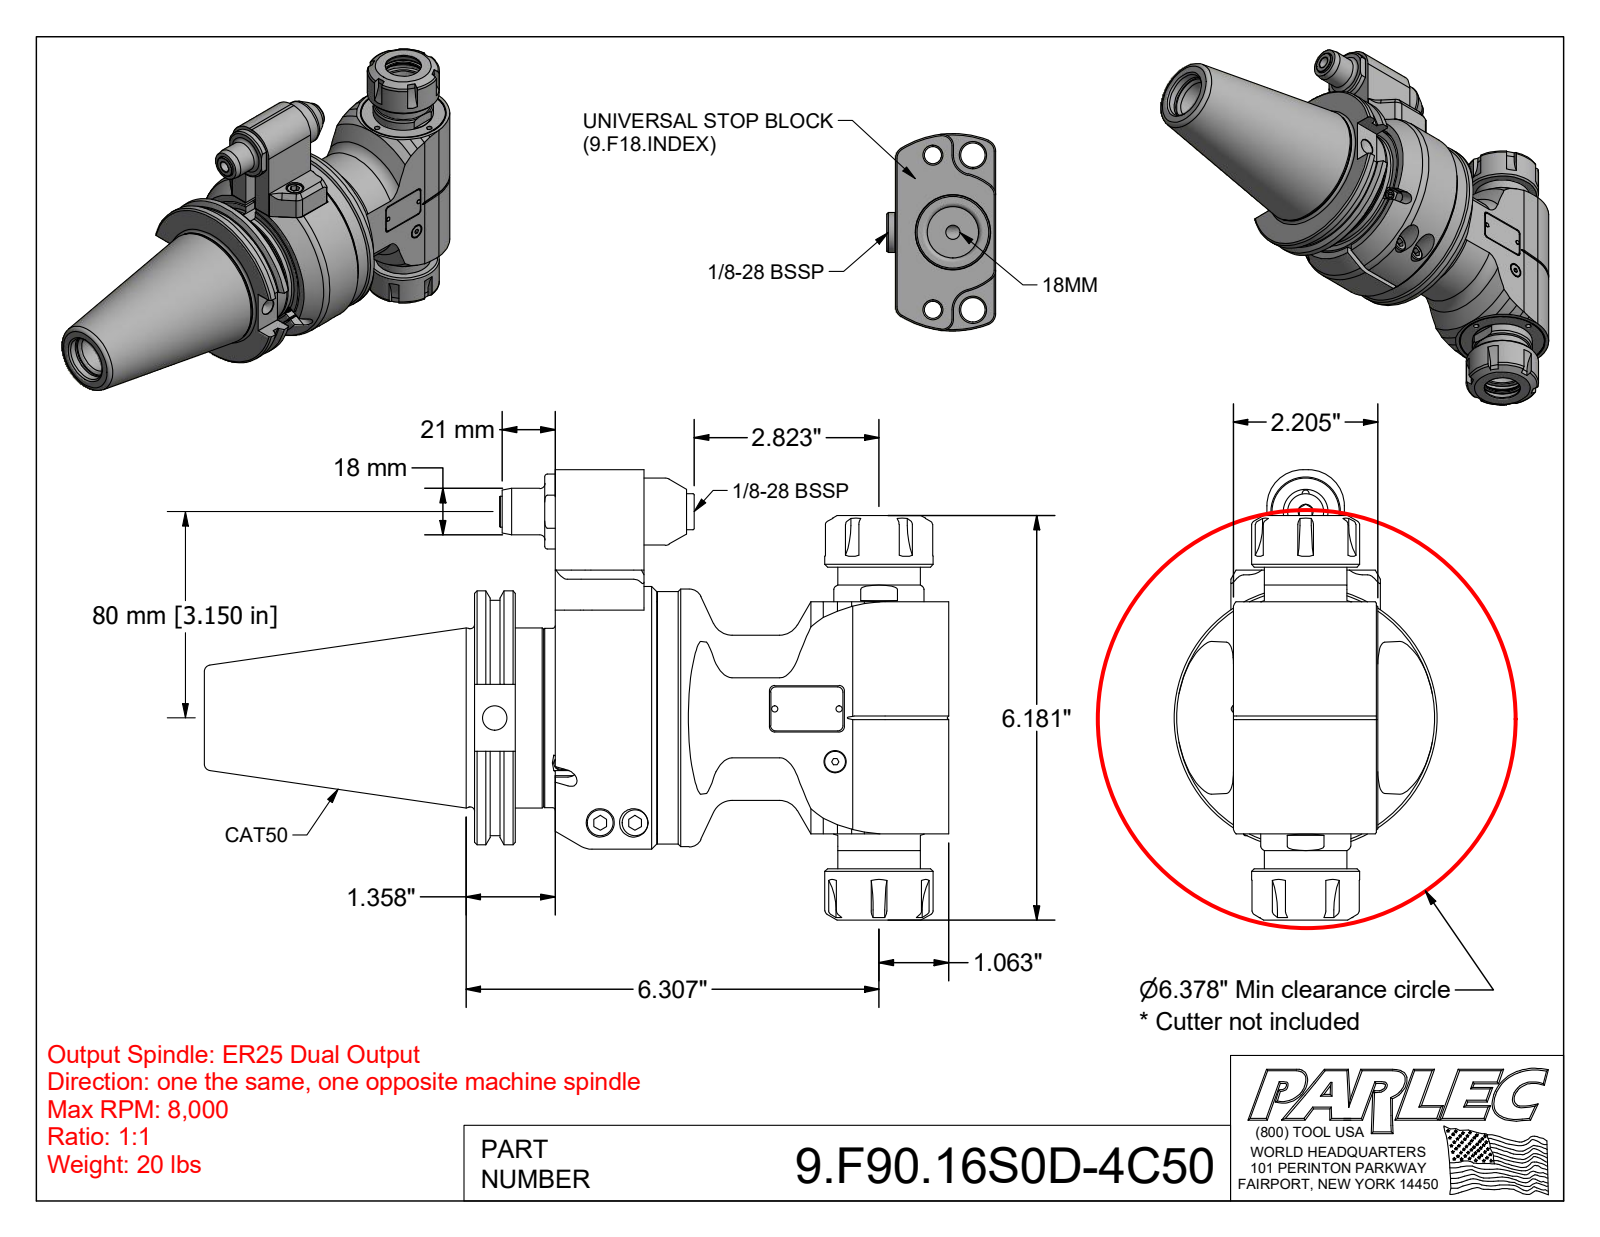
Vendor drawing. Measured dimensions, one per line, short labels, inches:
name: 9.F90.16S0D-4C50; 9_F90_16S00_2U; 9_GA1_458_2 (Type 1, Cat50, 80mm)
written by: Autodesk Inventor 2020 (AUTOMOTIVE_DESIGN)
unit: in
bodies: 5 solids, 570 faces (267 planar, 137 cylindrical, 166 other)
size: 11.37 × 6.88 × 4.016
volume: 79.8 in³; area: 267.9 in²
holes: 4× ⌀0.126, 2× ⌀0.102, 2× ⌀0.197, 2× ⌀0.409, 2× ⌀0.433, 2× ⌀1.063, 1× ⌀0.098, 1× ⌀0.118, 1× ⌀0.256, 1× ⌀0.276, 1× ⌀0.335, 1× ⌀0.375
bosses: 6× ⌀0.236, 4× ⌀0.394, 2× ⌀0.709, 2× ⌀0.315, 2× ⌀0.098, 1× ⌀4.016, 1× ⌀3.937, 1× ⌀3.875
rounds: 12× R0.079, 12× R0.984, 4× R0.157, 2× R0.016, 2× R0.02, 2× R0.039, 2× R0.138, 2× R0.197
face distances: 1.26, 1.252, 0.904, 0.911, 2.163, 0.625, 1.528, 1.536, 2.788, 1.233
hole spacings: 0.846, 1.197, 0.276, 1.693, 0.512, 0.551, 1.72, 2.272
